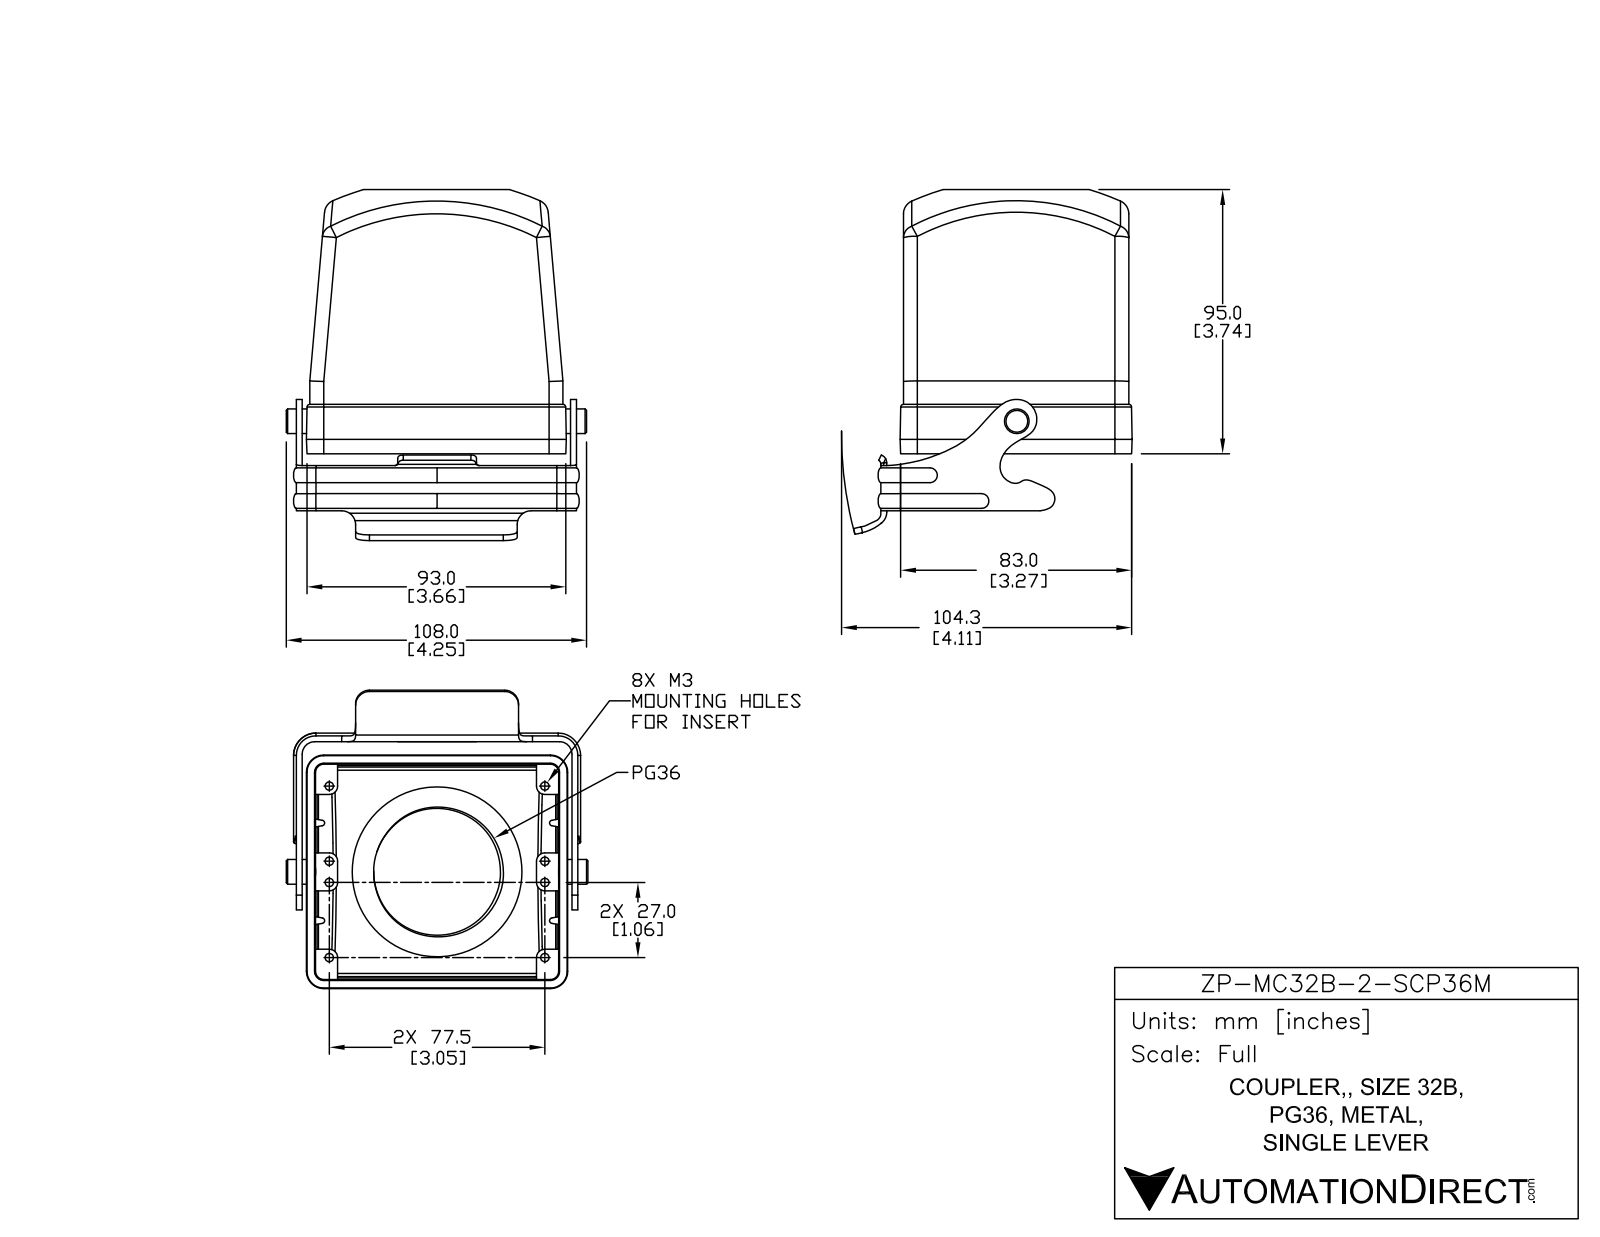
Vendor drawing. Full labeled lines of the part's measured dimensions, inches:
Part name (STEP PRODUCT): ZP-MC32B-2-SCP36M
STEP written by: SolidWorks 2014 (AUTOMOTIVE_DESIGN)
Units: inches
Bodies: 1 solid, 294 faces (123 planar, 102 cylindrical, 69 other)
Overall size (bounding box): 5.083 × 4.27 × 4.221
Volume: 8.698 in³ · Surface area: 132 in²
Round holes (diameter × count): ⌀0.118 ×8, ⌀0.104 ×1, ⌀1.795 ×1, ⌀2.087 ×1
Round bosses / shafts (diameter × count): ⌀2.402 ×1, ⌀0.348 ×1
Partial cylindrical surfaces — rounded edges, fillets, slot ends (radius × count): R0.197 ×13, R0.039 ×10, R0.118 ×9, R0.02 ×4, R0.079 ×2, R0.177 ×2, R0.278 ×2, R0.071 ×1
Main face-to-face distances: 0.122, 3.087, 3.209, 2.965, 0.083, 0.502, 3.317, 0.585, 3.4, 3.902
Hole centre spacings: 1.063, 1.364, 1.533, 1.949, 3.051, 3.231, 3.342, 0.301
